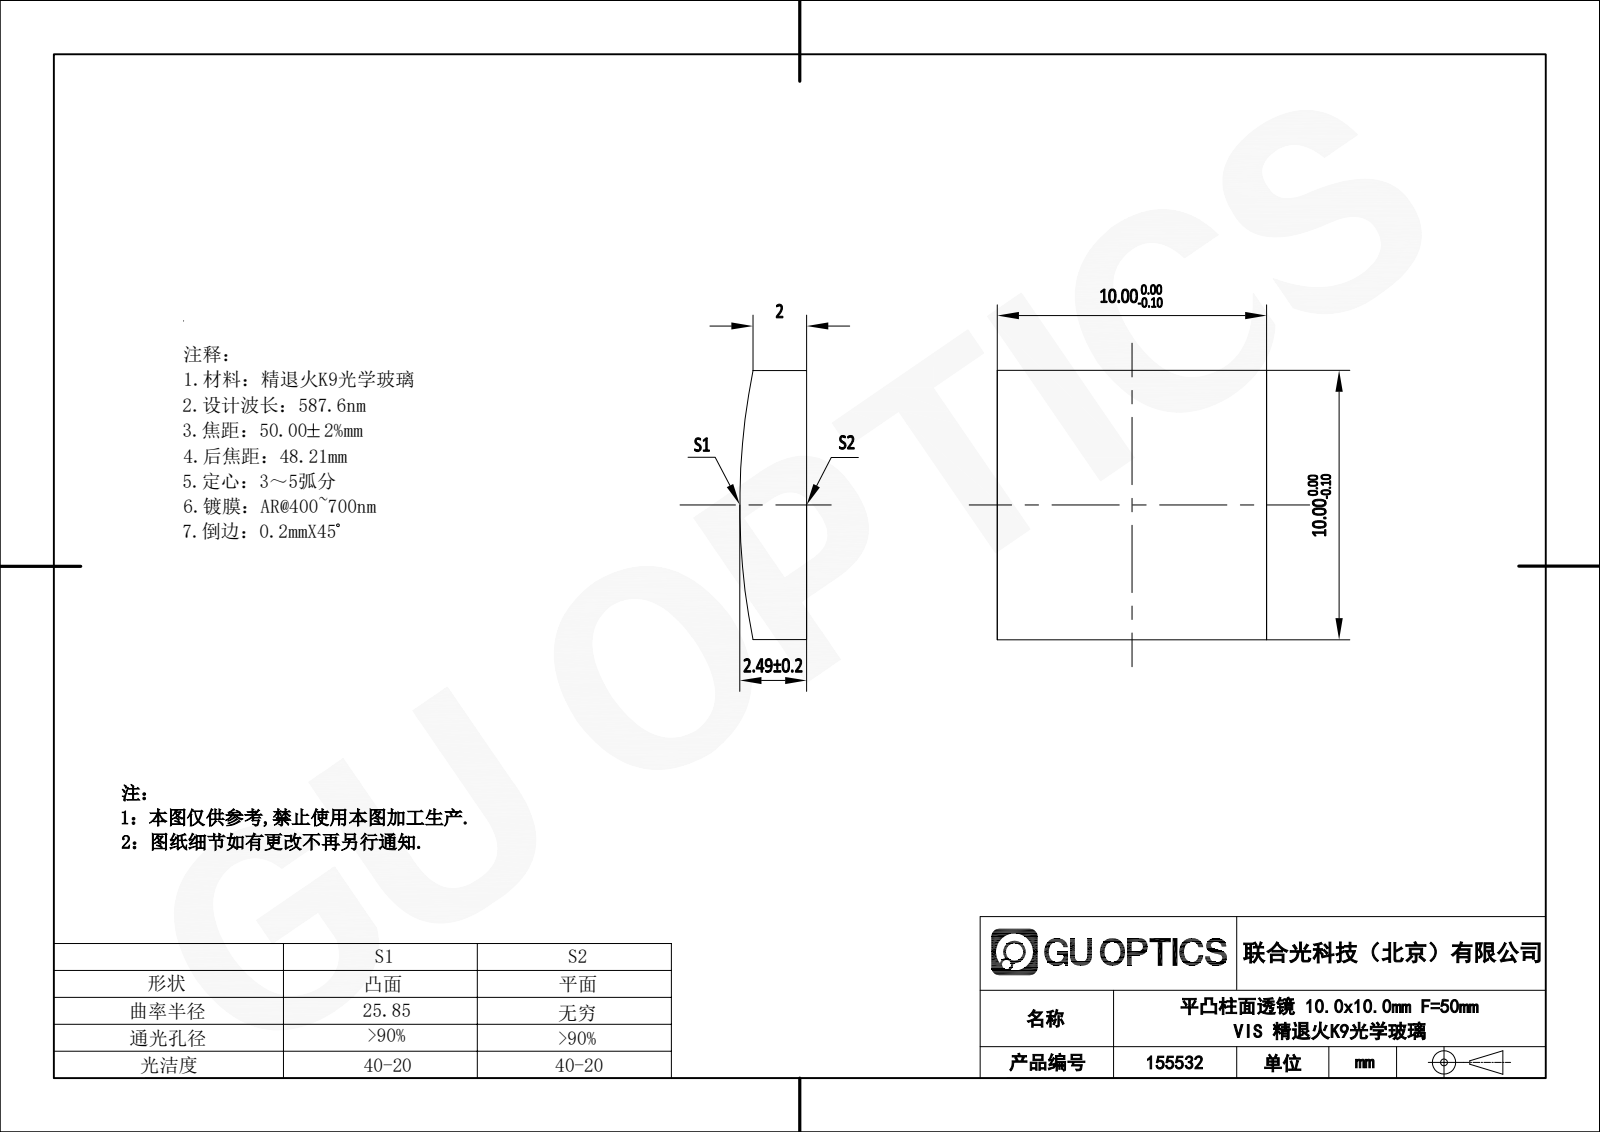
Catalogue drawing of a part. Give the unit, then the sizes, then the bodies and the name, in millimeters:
Units: millimetres
Overall size (bounding box): 10 × 10 × 2.49
Partial cylindrical surfaces — rounded edges, fillets, slot ends (radius × count): R25.85 ×1
Main face-to-face distances: 10
Volume: 233 mm³ · Surface area: 287 mm²
Bodies: 1 solid, 7 faces (5 planar, 2 cylindrical, 0 other)
Part name (STEP PRODUCT): 155520
STEP written by: SolidWorks 2020 (CONFIG_CONTROL_DESIGN)
